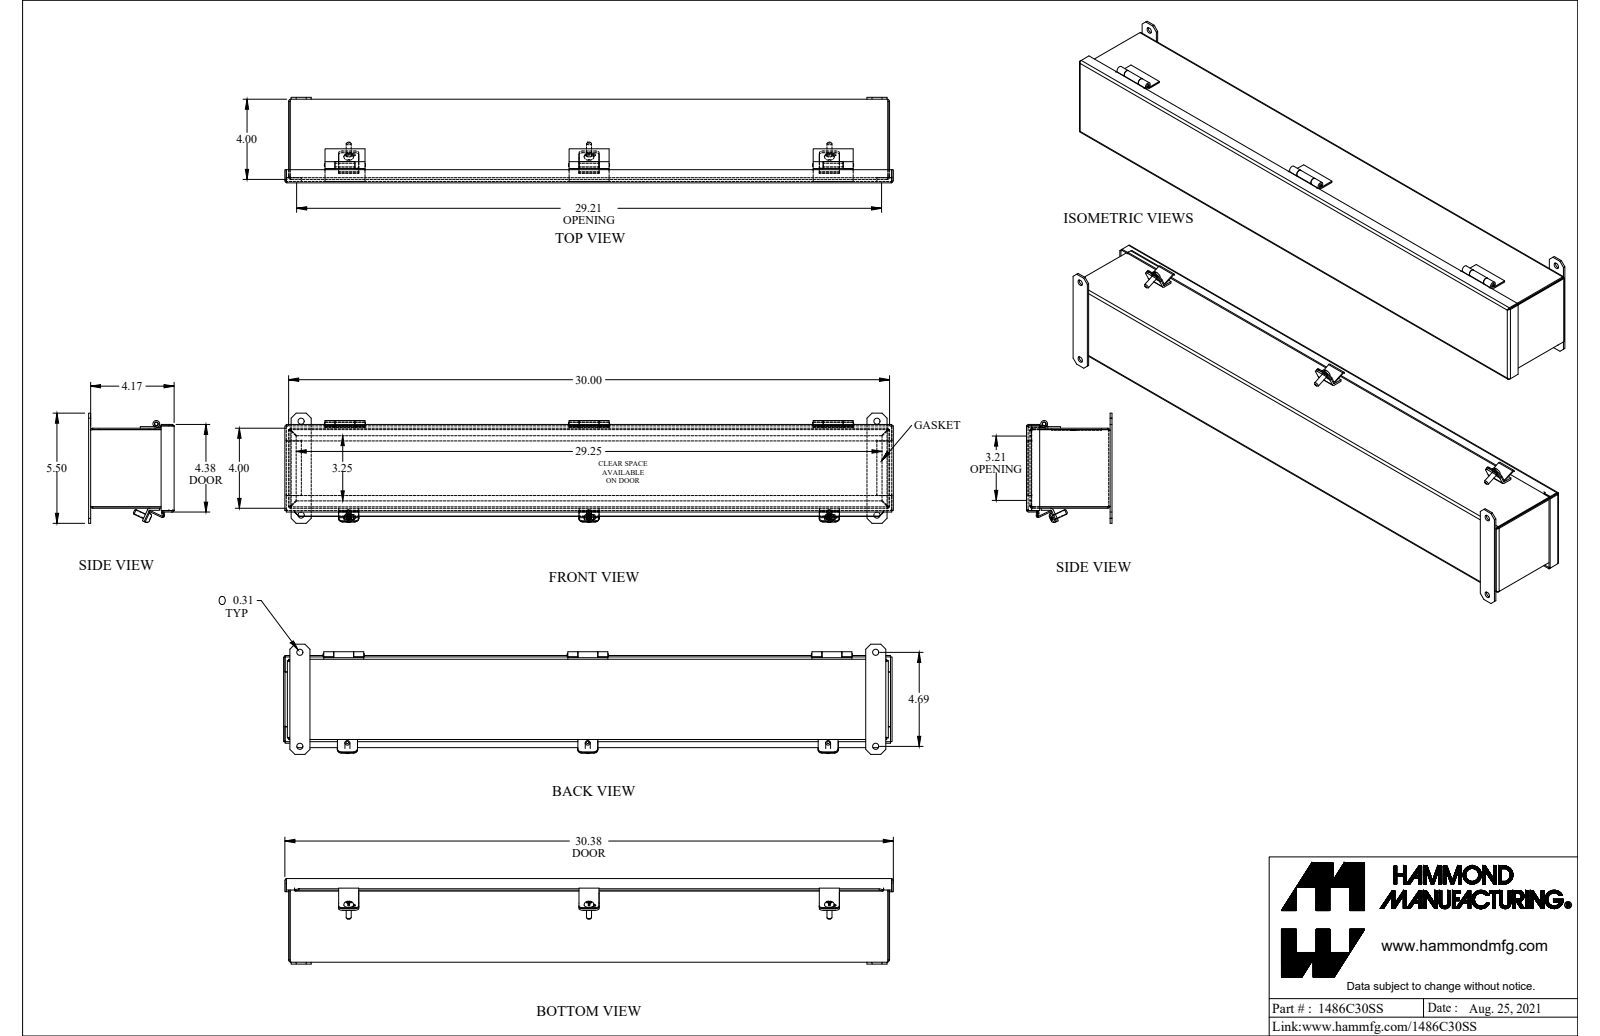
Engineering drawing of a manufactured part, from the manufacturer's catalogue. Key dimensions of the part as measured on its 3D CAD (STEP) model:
Part name (STEP PRODUCT): 1486C30SS
STEP written by: SolidWorks 2021 (AUTOMOTIVE_DESIGN)
Units: inches
Bodies: 9 solids, 536 faces (346 planar, 145 cylindrical, 45 other)
Overall size (bounding box): 30.375 × 5.5 × 4.267
Volume: 53.58 in³ · Surface area: 1 330 in²
Round holes (diameter × count): ⌀0.313 ×4, ⌀0.213 ×3, ⌀0.187 ×1
Round bosses / shafts (diameter × count): ⌀0.483 ×3, ⌀0.25 ×3, ⌀0.337 ×1, ⌀0.18 ×1
Partial cylindrical surfaces — rounded edges, fillets, slot ends (radius × count): R0.036 ×13, R0.108 ×13, R0.188 ×12, R0.25 ×12, R0.01 ×6, R0.03 ×6, R0.141 ×6, R0.029 ×2
Main face-to-face distances: 0.072, 3.928, 4.1, 3.856, 4, 4.028, 4.172, 0.187, 0.259, 3.913
Hole centre spacings: 4.688, 12, 24, 28.75, 28.75, 29.13, 29.13
